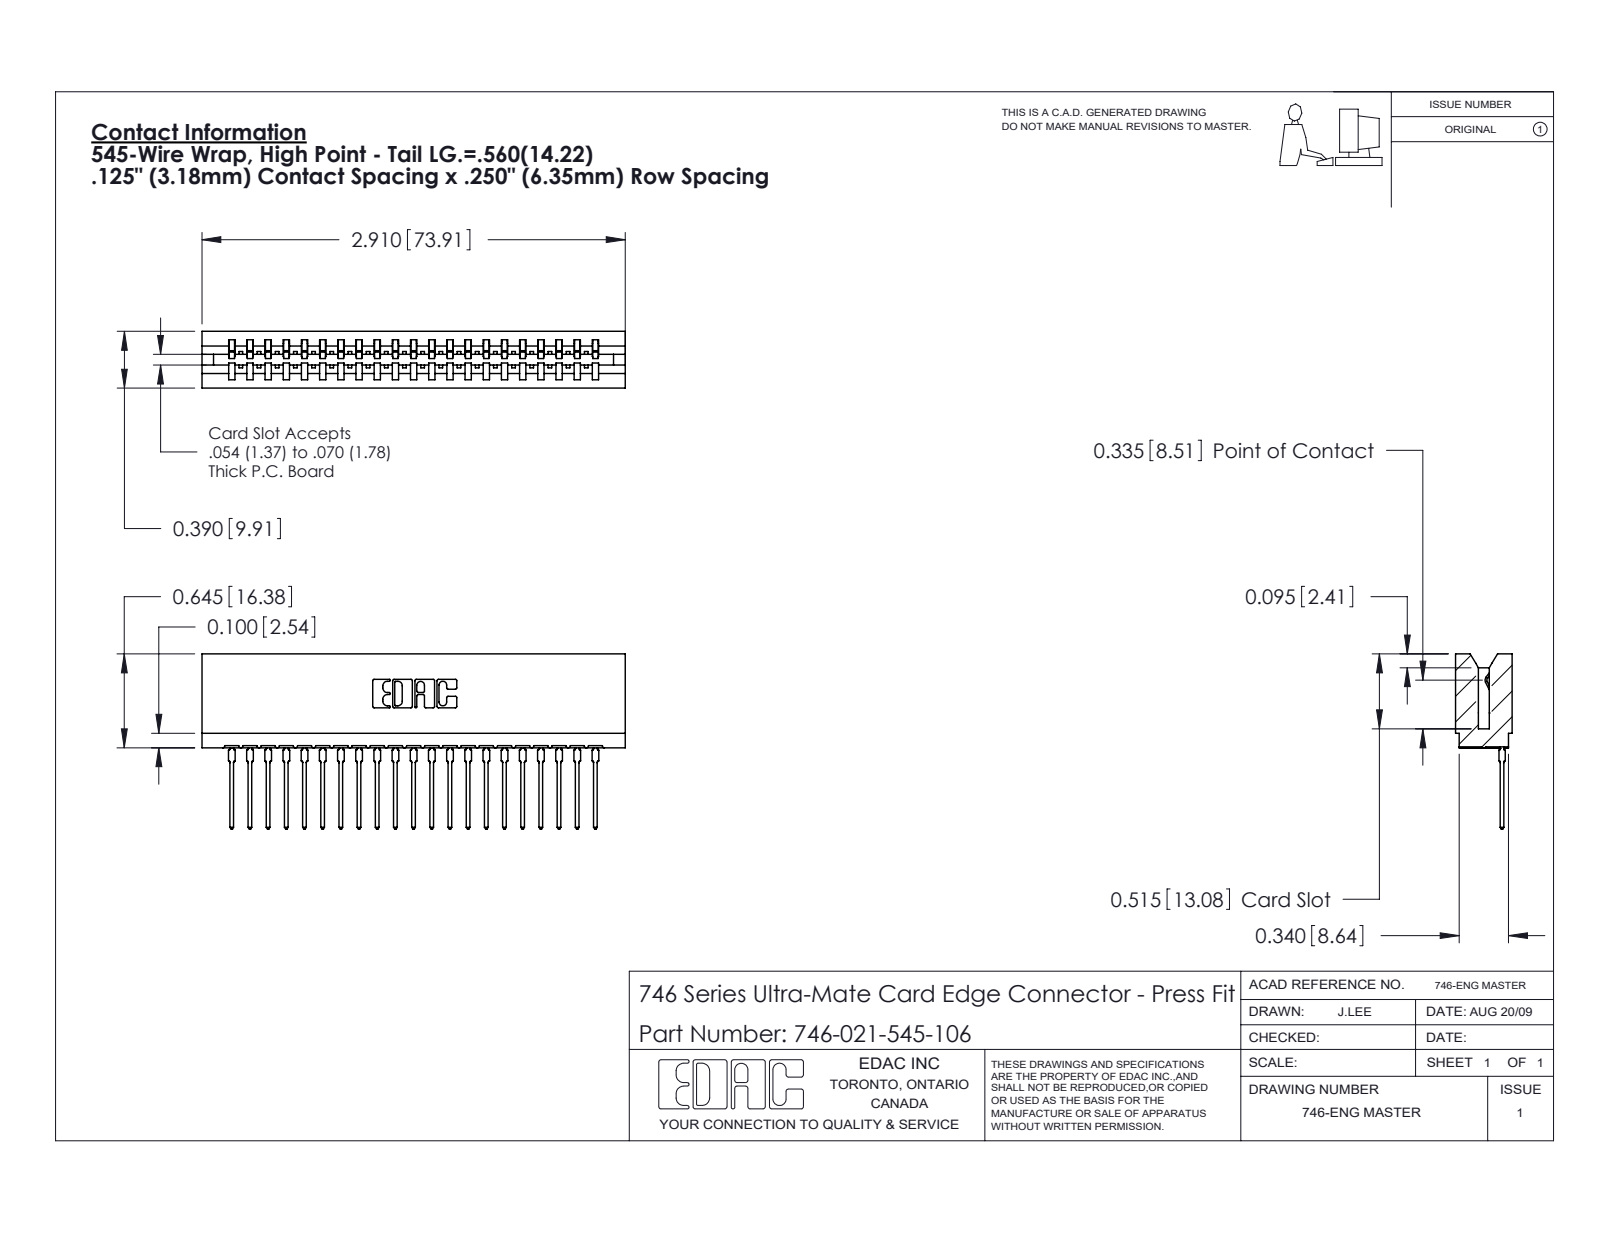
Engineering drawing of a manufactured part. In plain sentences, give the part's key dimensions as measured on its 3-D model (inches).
The part is named "746 Part_.515 Slot Depth - 06; 746-021-545-106; 746-292-001_545". Its 3-D file was written by "SolidWorks 2020 (CONFIG_CONTROL_DESIGN)". It is 22 solids with 2366 faces: 1379 planar, 441 cylindrical and 546 other. Overall it measures 2.91 by 1.204 by 0.39 inches. Its volume is 0.482 cubic inches and its surface area 18.09 square inches. Partial cylindrical surfaces (rounded edges, fillets, slot ends): 42 of radius 0.021, 22 of radius 0.01, 22 of radius 0.015, 6 of radius 0.007, 6 of radius 0.031, 4 of radius 0.005, 4 of radius 0.011, 3 of radius 0.026. The main face-to-face distances are 0.057, 0.333, 0.25, 0.39, 0.5, 0.025, 0.307, 0.083, 0.042, 0.125.
